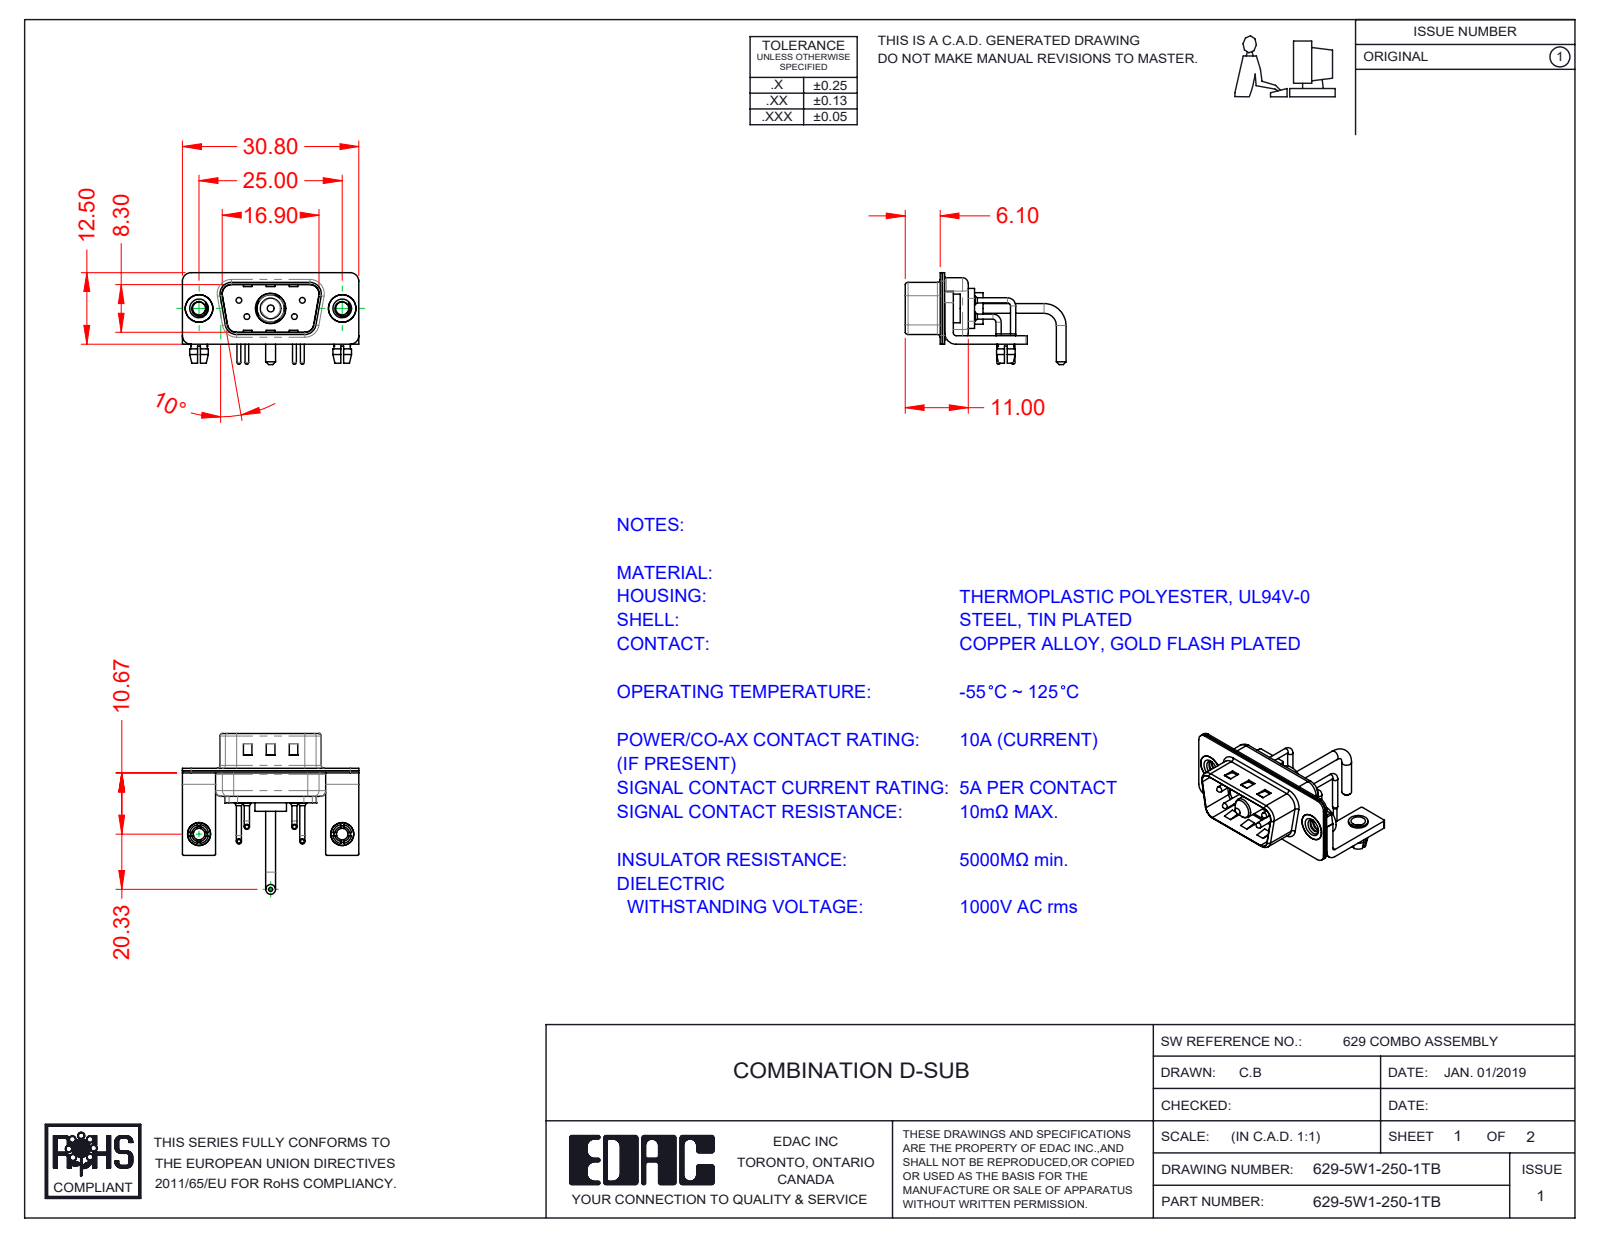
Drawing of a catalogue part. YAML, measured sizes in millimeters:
part_name: "629Combo Contact Row 1; 629Combo Shell Front_09 Contacts; 629Combo Contact Row 2; 629Combo Threaded Rivet_2 (+6 more)"
step_written_by: "SolidWorks 2020 (CONFIG_CONTROL_DESIGN)"
units: millimeters
bodies: {solids: 15, faces: 927, planar: 441, cylindrical: 350, other: 136}
overall_size: [30.8, 28.08, 16.05]
volume: 1784
surface_area: 4612
round_holes:
  - {diameter: 2, count: 6}
  - {diameter: 0.75, count: 4}
  - {diameter: 1.6, count: 4}
  - {diameter: 2.26, count: 2}
  - {diameter: 2.5, count: 2}
  - {diameter: 3.2, count: 2}
  - {diameter: 4, count: 2}
  - {diameter: 4.8, count: 2}
  - {diameter: 4.85, count: 1}
  - {diameter: 5.3, count: 1}
round_bosses_or_shafts:
  - {diameter: 0.9, count: 8}
  - {diameter: 1.5, count: 4}
  - {diameter: 1, count: 4}
  - {diameter: 0.65, count: 4}
  - {diameter: 5, count: 2}
  - {diameter: 4.9, count: 2}
  - {diameter: 4, count: 2}
  - {diameter: 3.4, count: 2}
partial_cylinders:
  - {radius: 0.25, count: 16}
  - {radius: 1.5, count: 16}
  - {radius: 2, count: 13}
  - {radius: 0.5, count: 9}
  - {radius: 1.6, count: 8}
  - {radius: 0.6, count: 4}
  - {radius: 0.65, count: 4}
  - {radius: 0.9, count: 4}
face_to_face_distances: [0.4, 0.8, 1.5, 9.5, 9.1, 1.2, 0.65, 9.9, 8.7, 0.6]
hole_center_spacings: [3.16, 5.72, 7.1, 12.5, 18.1, 25, 4.39, 4.4]
